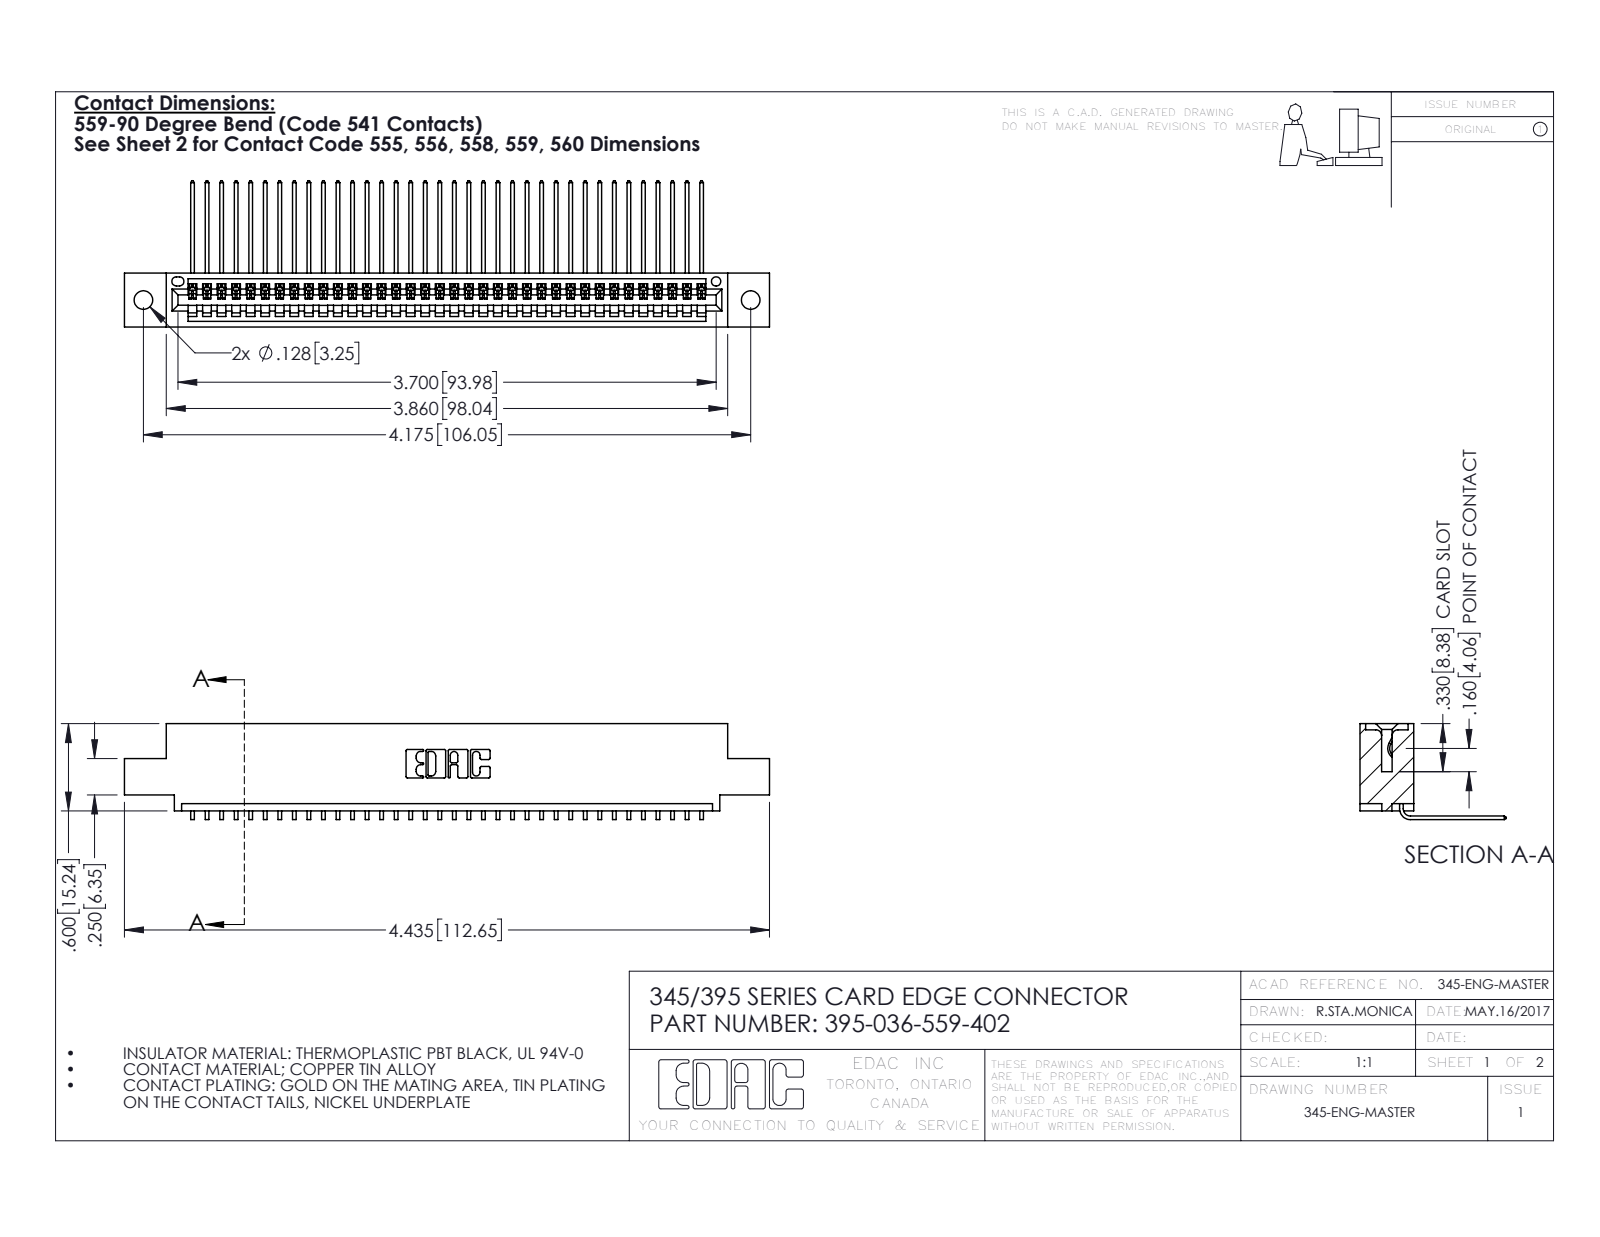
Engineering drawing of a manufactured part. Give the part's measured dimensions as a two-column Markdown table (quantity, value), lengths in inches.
| quantity | value |
| --- | --- |
| part name | 395-036-559-402; 345-292-001_558 559 Tail - 1; 345 Part_0.110 Offset - 0.128 Dia |
| STEP written by | SolidWorks 2016 (CONFIG_CONTROL_DESIGN) |
| units | inches |
| bodies | 37 solids, 2290 faces (1596 planar, 694 cylindrical, 0 other) |
| overall size | 4.435 × 1.005 × 0.659 |
| volume | 0.651 in³ |
| surface area | 22.63 in² |
| round holes (diameter × count) | 0.128 × 2, 0.064 × 1 |
| partial cylindrical surfaces (radius × count) | 0.006 × 72, 0.01 × 22, 0.007 × 6, 0.031 × 6, 0.026 × 3, 0.031 × 2, 0.04 × 2, 0.014 × 1 |
| main face-to-face distances | 0.072, 0.298, 0.37, 0.2, 0.098, 0.272, 0.025, 0.225, 0.149, 0.072 |
| hole center spacings | 0.27, 3.939, 4.175 |
